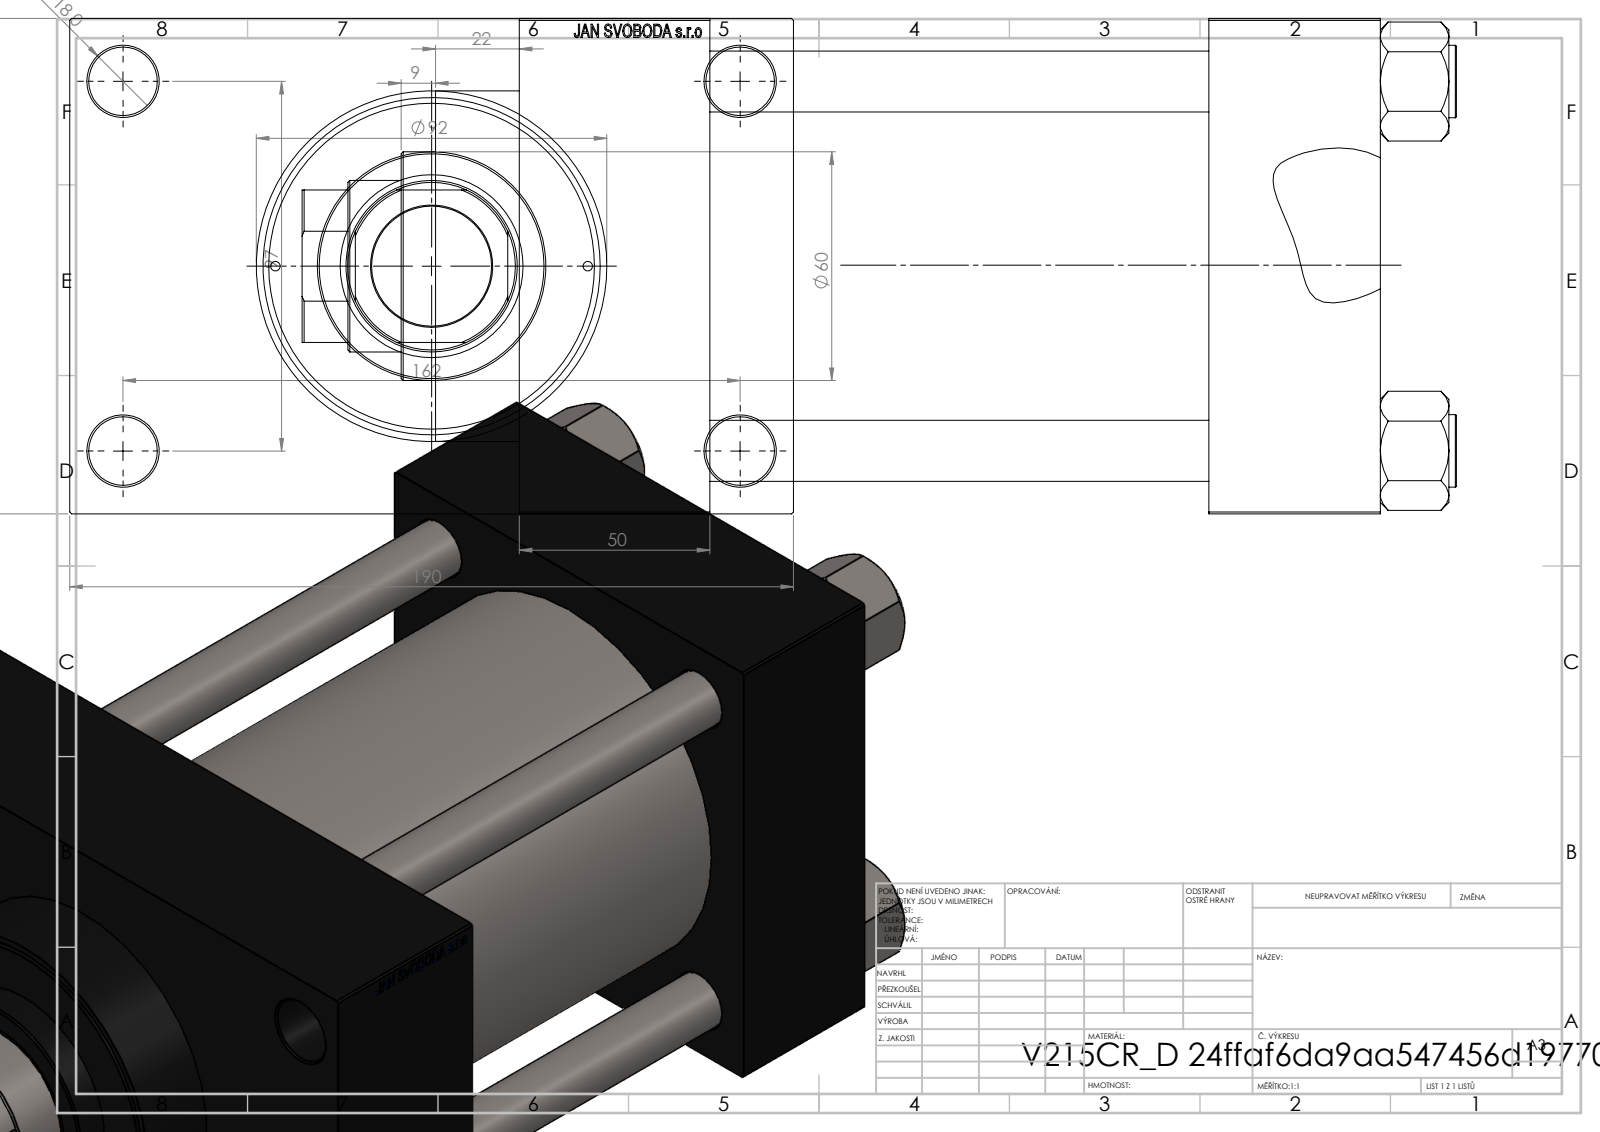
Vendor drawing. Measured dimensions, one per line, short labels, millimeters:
name: V215CR_D_TYCINKA; V215CR_D_Body; V215_VC_A; V215CR_VCP_D (+1 more)
written by: SolidWorks 2019 (CONFIG_CONTROL_DESIGN)
unit: mm
bodies: 11 solids, 1159 faces (547 planar, 92 cylindrical, 520 other)
size: 303 × 190 × 130
volume: 2 792 000 mm³; area: 414 099 mm²
holes: 4× ⌀16, 4× ⌀18, 2× ⌀2.5, 2× ⌀7, 2× ⌀26.44, 2× ⌀35, 1× ⌀31.5, 1× ⌀45, 1× ⌀48, 1× ⌀76, 1× ⌀85.5, 1× ⌀100
bosses: 4× ⌀19, 1× ⌀106, 1× ⌀92, 1× ⌀60
rounds: 1× R22
face distances: 130, 45, 176, 131, 226, 181, 50, 30, 160, 80
hole spacings: 32.55, 49.02, 62.87, 68.52, 94.41, 96.9, 101.73, 102.27
